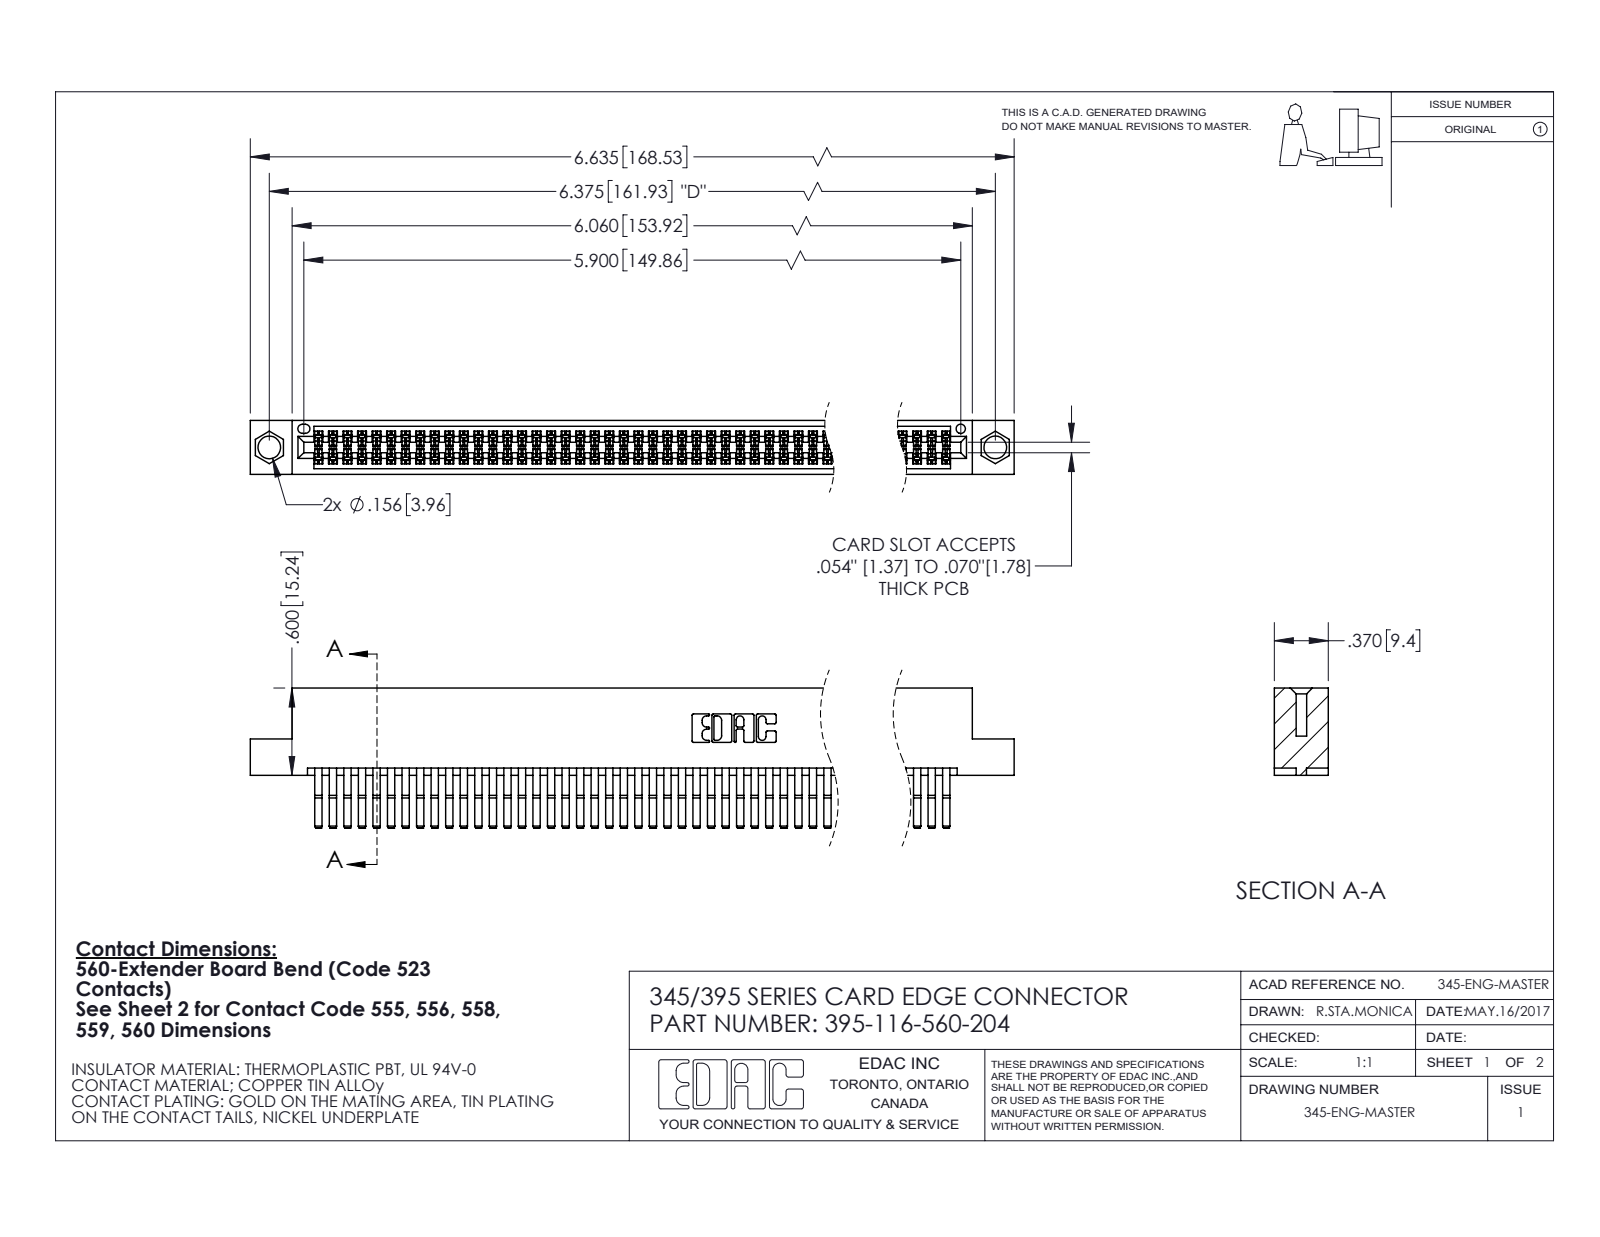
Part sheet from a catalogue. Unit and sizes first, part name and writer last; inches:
Units: inches
Overall size (bounding box): 6.635 × 0.962 × 0.37
Round holes (diameter × count): ⌀0.156 ×2, ⌀0.064 ×1
Partial cylindrical surfaces — rounded edges, fillets, slot ends (radius × count): R0.006 ×174, R0.01 ×22, R0.007 ×6, R0.031 ×6, R0.026 ×3, R0.01 ×2, R0.014 ×2, R0.019 ×2
Main face-to-face distances: 0.025, 0.298, 0.072, 0.37, 0.2, 0.098, 0.272, 0.225, 0.175, 0.149
Hole centre spacings: 0.27, 6.139, 6.375
Volume: 1.048 in³ · Surface area: 42.63 in²
Bodies: 117 solids, 6172 faces (3922 planar, 2250 cylindrical, 0 other)
Part name (STEP PRODUCT): 395-116-560-204; 345-292-001_560 Tail; 345 Part_Flush Mounting Lugs - 0.156 Dia-TI
STEP written by: SolidWorks 2020 (CONFIG_CONTROL_DESIGN)
